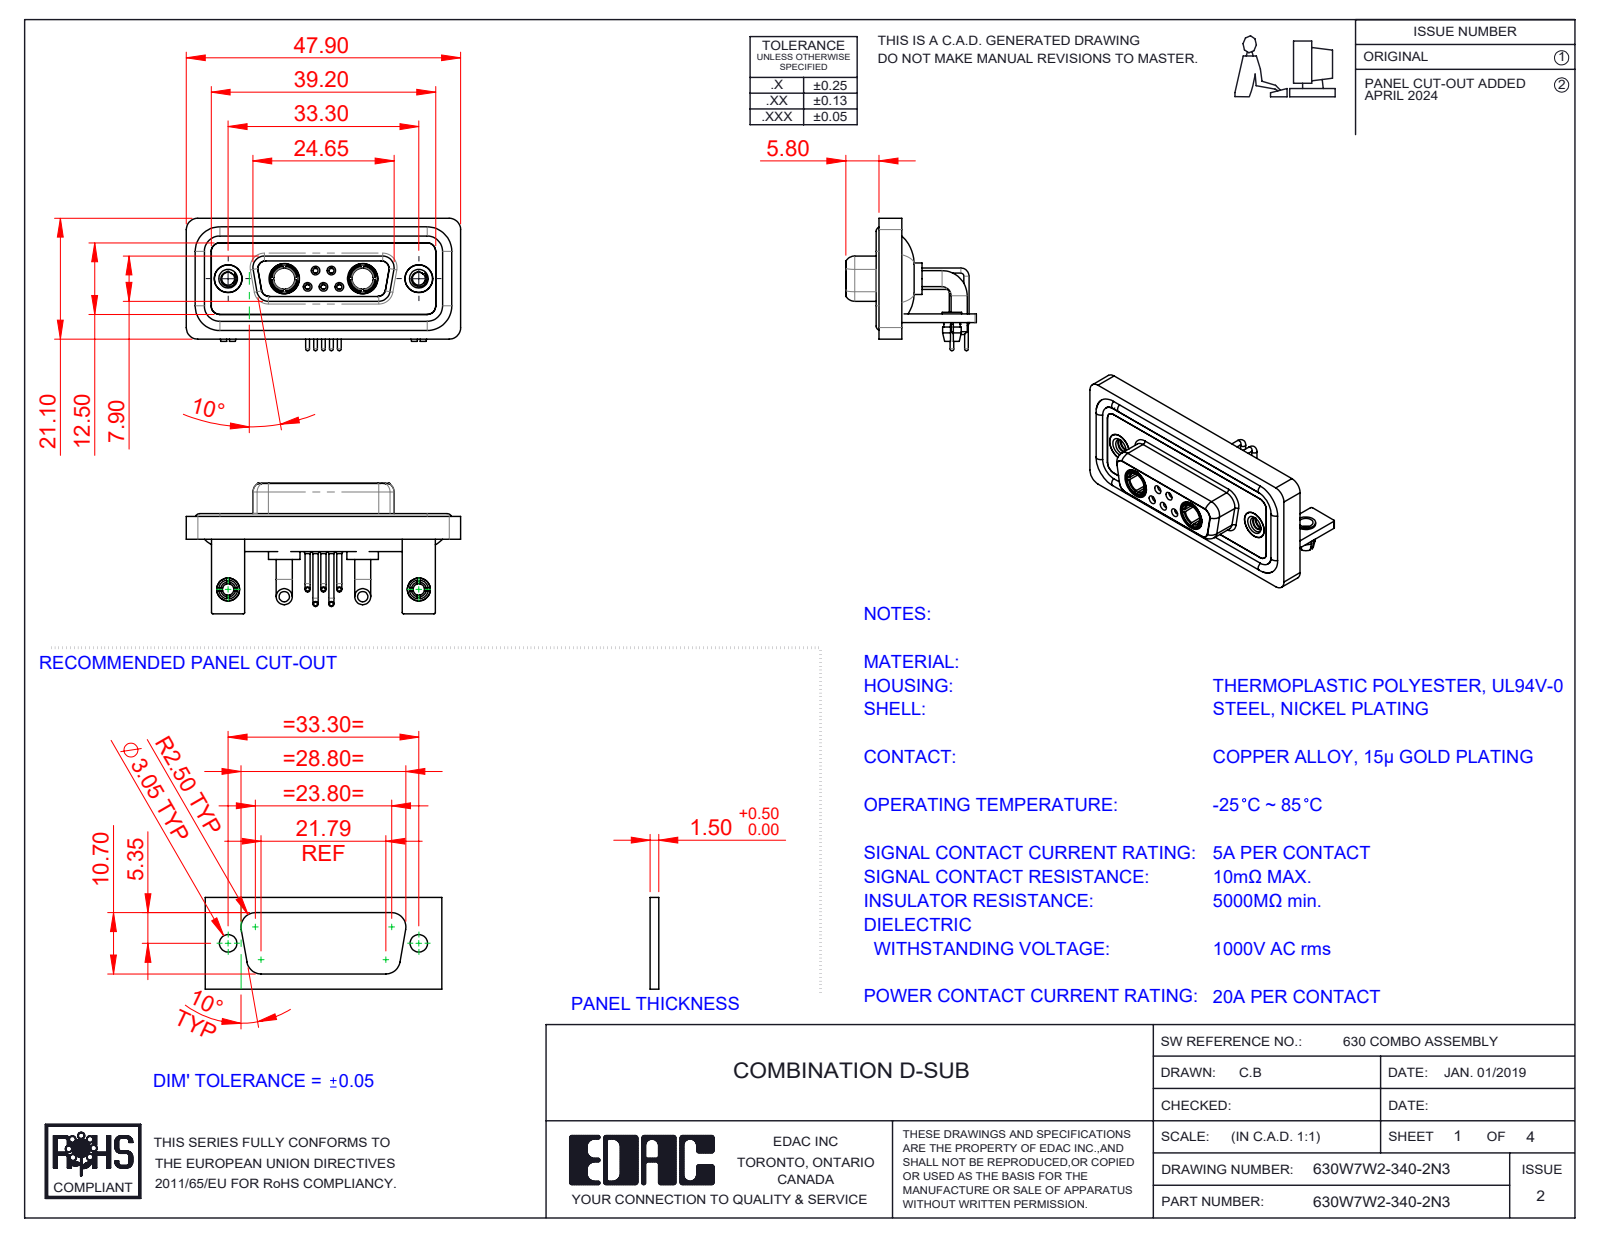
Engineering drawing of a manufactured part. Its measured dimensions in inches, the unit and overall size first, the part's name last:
Units: inches
Overall size (bounding box): 1.886 × 0.91 × 0.898
Round holes (diameter × count): ⌀0.079 ×7, ⌀0.035 ×5, ⌀0.043 ×5, ⌀0.059 ×5, ⌀0.191 ×4, ⌀0.063 ×3, ⌀0.067 ×2, ⌀0.089 ×2, ⌀0.098 ×2, ⌀0.126 ×2, ⌀0.146 ×2, ⌀0.157 ×2
Round bosses / shafts (diameter × count): ⌀0.063 ×6, ⌀0.035 ×5, ⌀0.026 ×5, ⌀0.11 ×4, ⌀0.217 ×2, ⌀0.205 ×2, ⌀0.195 ×2, ⌀0.195 ×2
Partial cylindrical surfaces — rounded edges, fillets, slot ends (radius × count): R0.079 ×21, R0.059 ×18, R0.01 ×16, R0.053 ×12, R0.063 ×8, R0.02 ×5, R0.024 ×4, R0.026 ×4
Main face-to-face distances: 0.016, 0.114, 0.059, 0.071, 0.146, 0.043, 0.161, 0.063, 0.098, 0.055
Hole centre spacings: 0.124, 0.109, 0.386, 0.925, 1.311, 0.17, 0.17, 0.198
Volume: 0.403 in³ · Surface area: 17.28 in²
Bodies: 20 solids, 947 faces (306 planar, 409 cylindrical, 232 other)
Part name (STEP PRODUCT): 630Combo Housing_7W2; 630Combo Stabilizer Bracket_50 Contacts; Power Socket_20A RA; 630Combo Shell Front_15 Contacts (+7 more)
STEP written by: SolidWorks 2023 (CONFIG_CONTROL_DESIGN)
